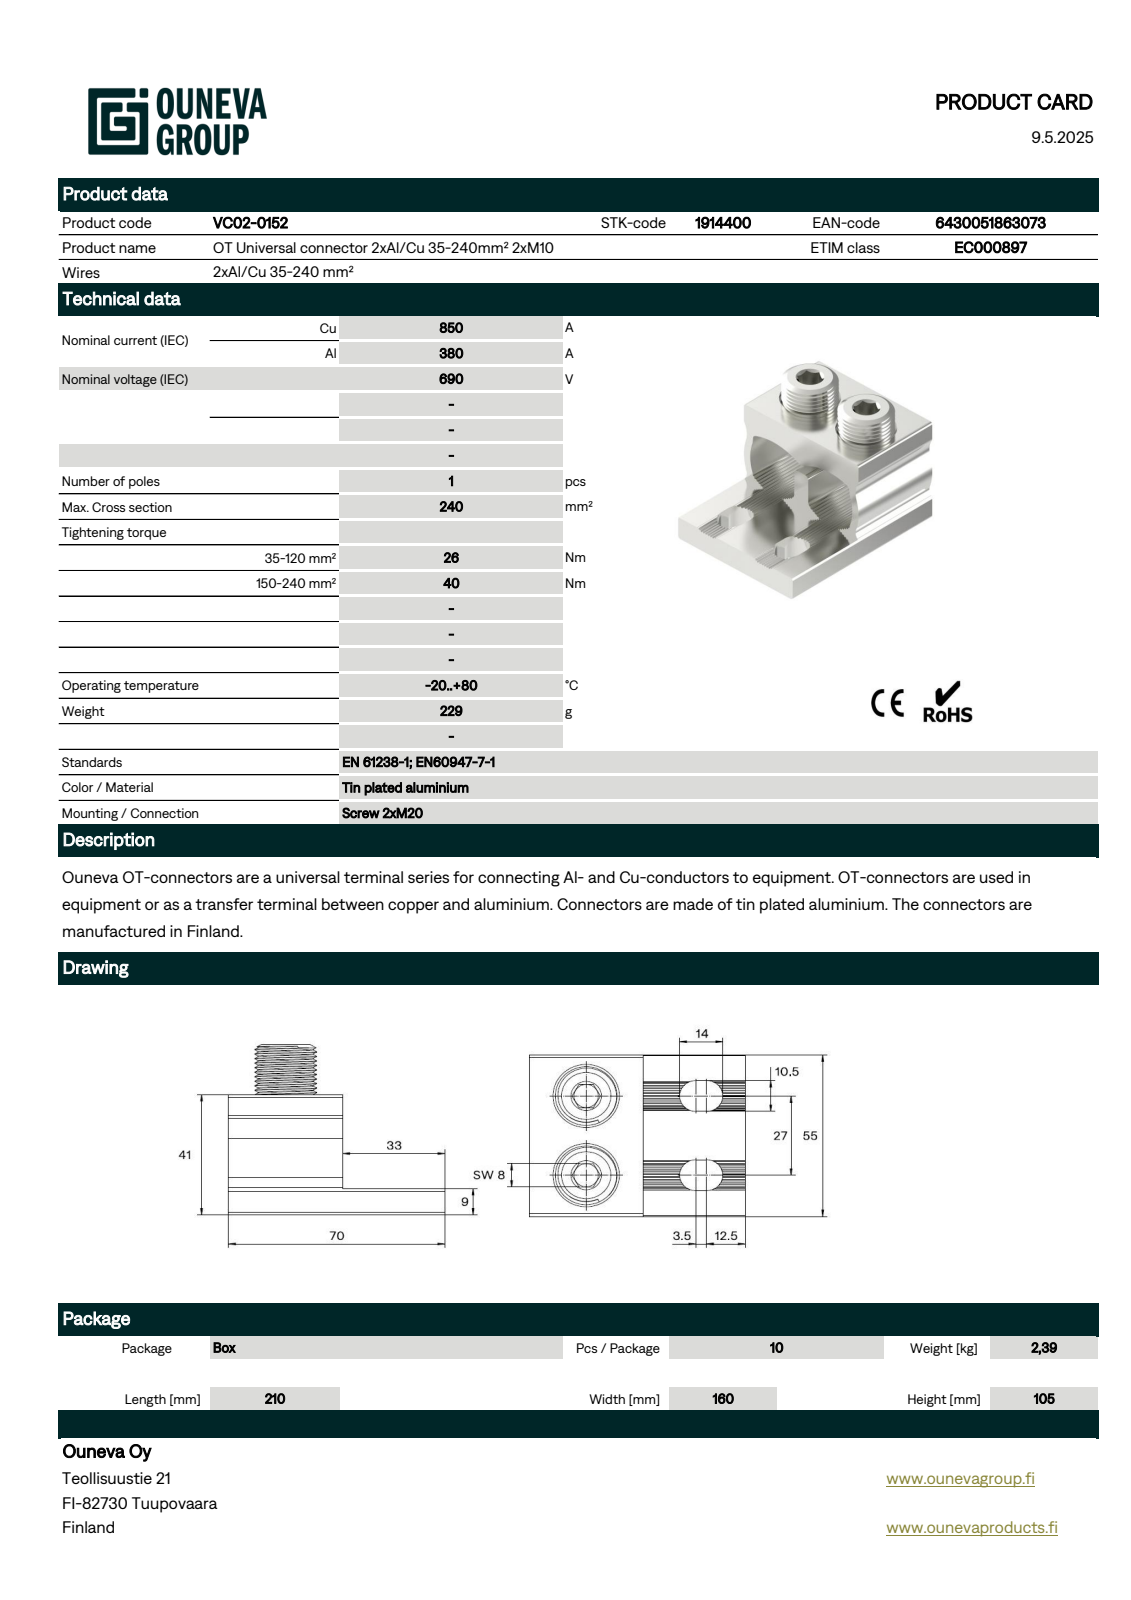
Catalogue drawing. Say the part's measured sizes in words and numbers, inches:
The part is named "VC02-0152_OT_2x240_2xM10". Its 3-D file was written by "Creo Elements/Direct Modeling 20.6A 14-Oct-2023 (C) Parametric Technology GmbH (AUTOMOTIVE_DESIGN)". It is 1 solid with 215 faces: 52 planar, 151 cylindrical and 12 other. Overall it measures 2.756 by 2.283 by 2.165 inches. Its volume is 4.418 cubic inches and its surface area 36.45 square inches. Round bosses or shafts: 2 of diameter 0.787. Partial cylindrical surfaces (rounded edges, fillets, slot ends): 74 of radius 0.012, 6 of radius 0.079, 4 of radius 0.039, 4 of radius 0.059, 4 of radius 0.207, 2 of radius 0.118, 2 of radius 0.138, 2 of radius 0.256. The main face-to-face distances are 1.614, 0.354, 1.26, 1.457, 2.165, 0.95, 1.215, 2.756, 1.299, 0.315.
